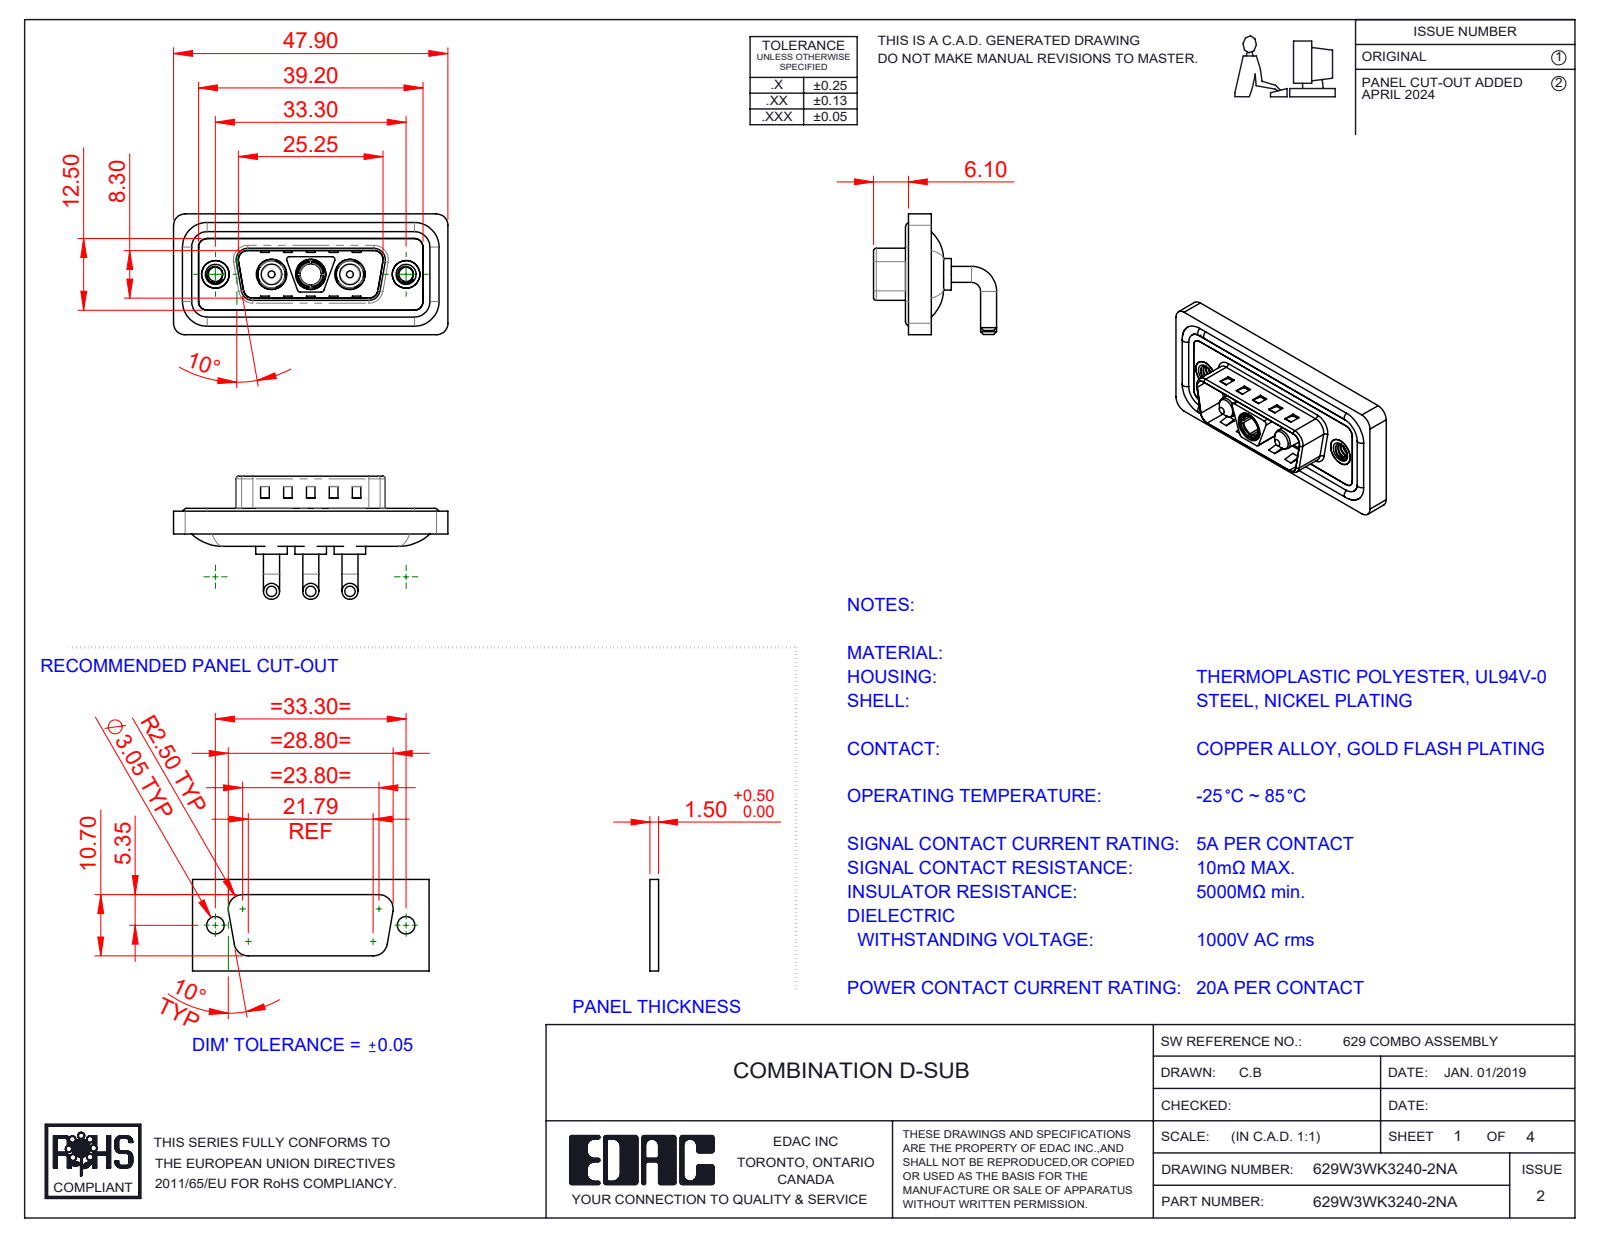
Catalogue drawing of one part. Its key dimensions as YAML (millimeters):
part_name: "629Combo Housing_3WK3; 629Combo Shell Rear_15 Contacts; Power Pin_20A RA; 629W3WK3140-2NA (+4 more)"
step_written_by: "SolidWorks 2023 (CONFIG_CONTROL_DESIGN)"
units: millimeters
bodies: {solids: 13, faces: 615, planar: 231, cylindrical: 254, other: 130}
overall_size: [47.9, 21.5, 21.1]
volume: 5888
surface_area: 9419
round_holes:
  - {diameter: 4.85, count: 3}
  - {diameter: 5.3, count: 3}
  - {diameter: 2.5, count: 2}
  - {diameter: 4, count: 2}
  - {diameter: 4.8, count: 2}
  - {diameter: 5, count: 2}
  - {diameter: 3.7, count: 1}
round_bosses_or_shafts:
  - {diameter: 2.8, count: 6}
  - {diameter: 1.6, count: 4}
  - {diameter: 5.5, count: 3}
  - {diameter: 5.2, count: 3}
  - {diameter: 4.75, count: 3}
  - {diameter: 3.75, count: 3}
  - {diameter: 4.9, count: 2}
  - {diameter: 3.6, count: 2}
partial_cylinders:
  - {radius: 2, count: 20}
  - {radius: 1.5, count: 18}
  - {radius: 0.5, count: 12}
  - {radius: 1.6, count: 8}
  - {radius: 0.25, count: 4}
  - {radius: 0.6, count: 4}
  - {radius: 0.65, count: 4}
  - {radius: 0.9, count: 4}
face_to_face_distances: [0.4, 2.9, 0.8, 1.1, 2.1, 1.6, 4.5, 3.1, 2.5, 3.7]
hole_center_spacings: [6.85, 9.8, 16.65, 23.5, 13.7, 33.3]
